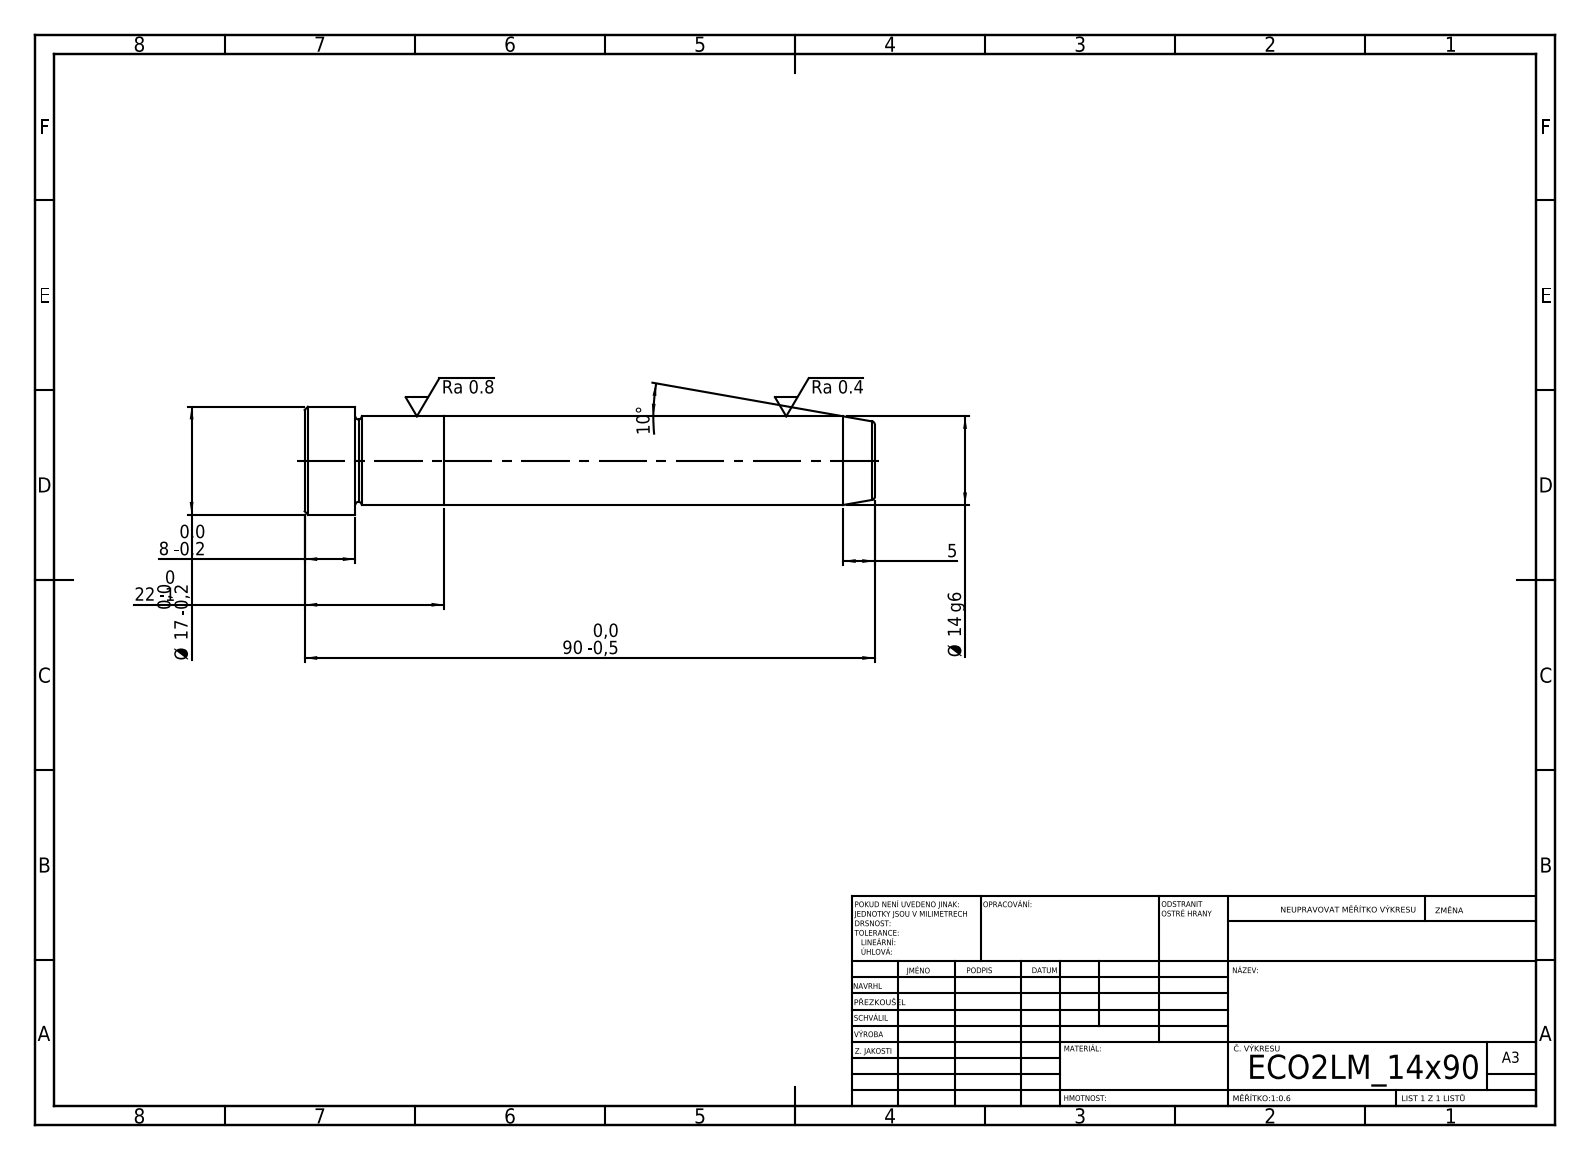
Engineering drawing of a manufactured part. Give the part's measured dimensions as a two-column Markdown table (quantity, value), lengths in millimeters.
| quantity | value |
| --- | --- |
| STEP written by | SolidWorks 2019 (CONFIG_CONTROL_DESIGN) |
| units | millimeters |
| bodies | 2 solids, 21 faces (5 planar, 6 cylindrical, 10 other) |
| overall size | 90 × 17 × 17 |
| volume | 14 321 mm³ |
| surface area | 4 749 mm² |
| round bosses / shafts (diameter × count) | 17 × 1, 14 × 1 |
| main face-to-face distances | 22, 68, 90, 82, 14, 8 |
